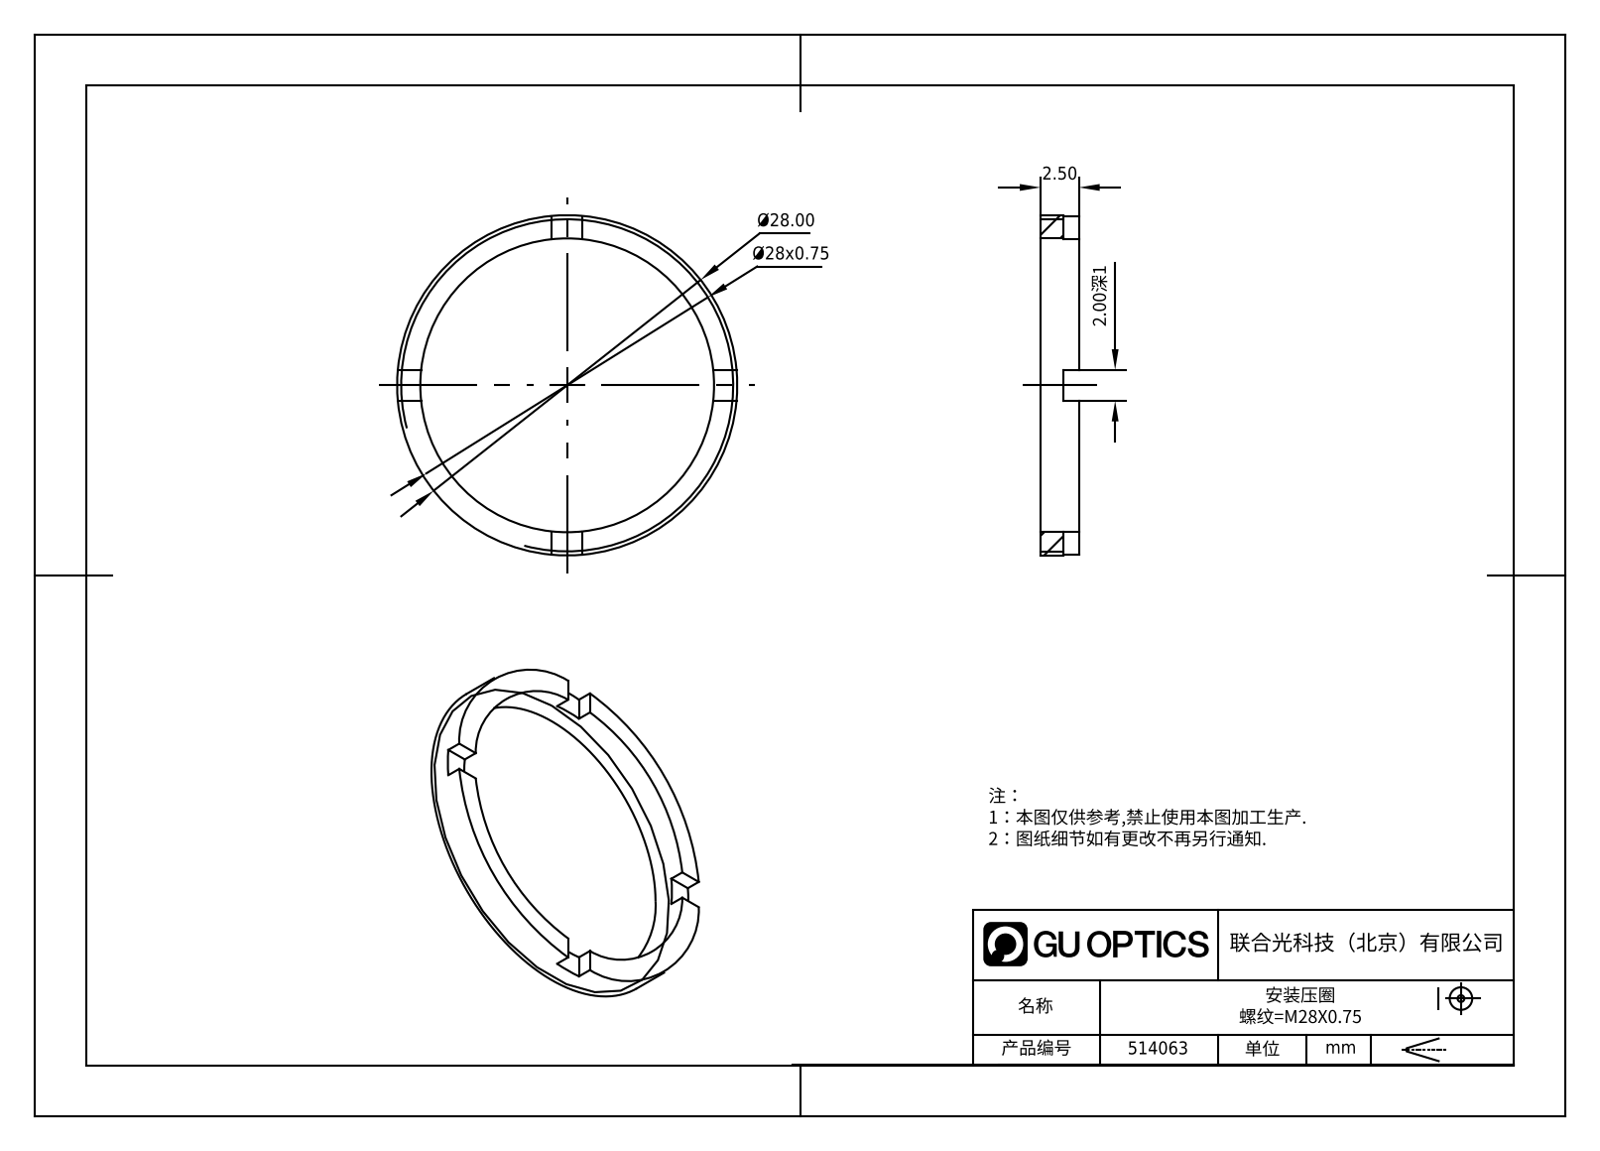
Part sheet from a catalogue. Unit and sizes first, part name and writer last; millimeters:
Units: millimetres
Overall size (bounding box): 28 × 28 × 2.5
Round holes (diameter × count): ⌀25 ×1
Round bosses / shafts (diameter × count): ⌀28 ×1
Main face-to-face distances: 2.5, 1.5, 1, 2
Volume: 300 mm³ · Surface area: 662 mm²
Bodies: 1 solid, 21 faces (17 planar, 4 cylindrical, 0 other)
Part name (STEP PRODUCT): 514063
STEP written by: SolidWorks 2020 (CONFIG_CONTROL_DESIGN)
